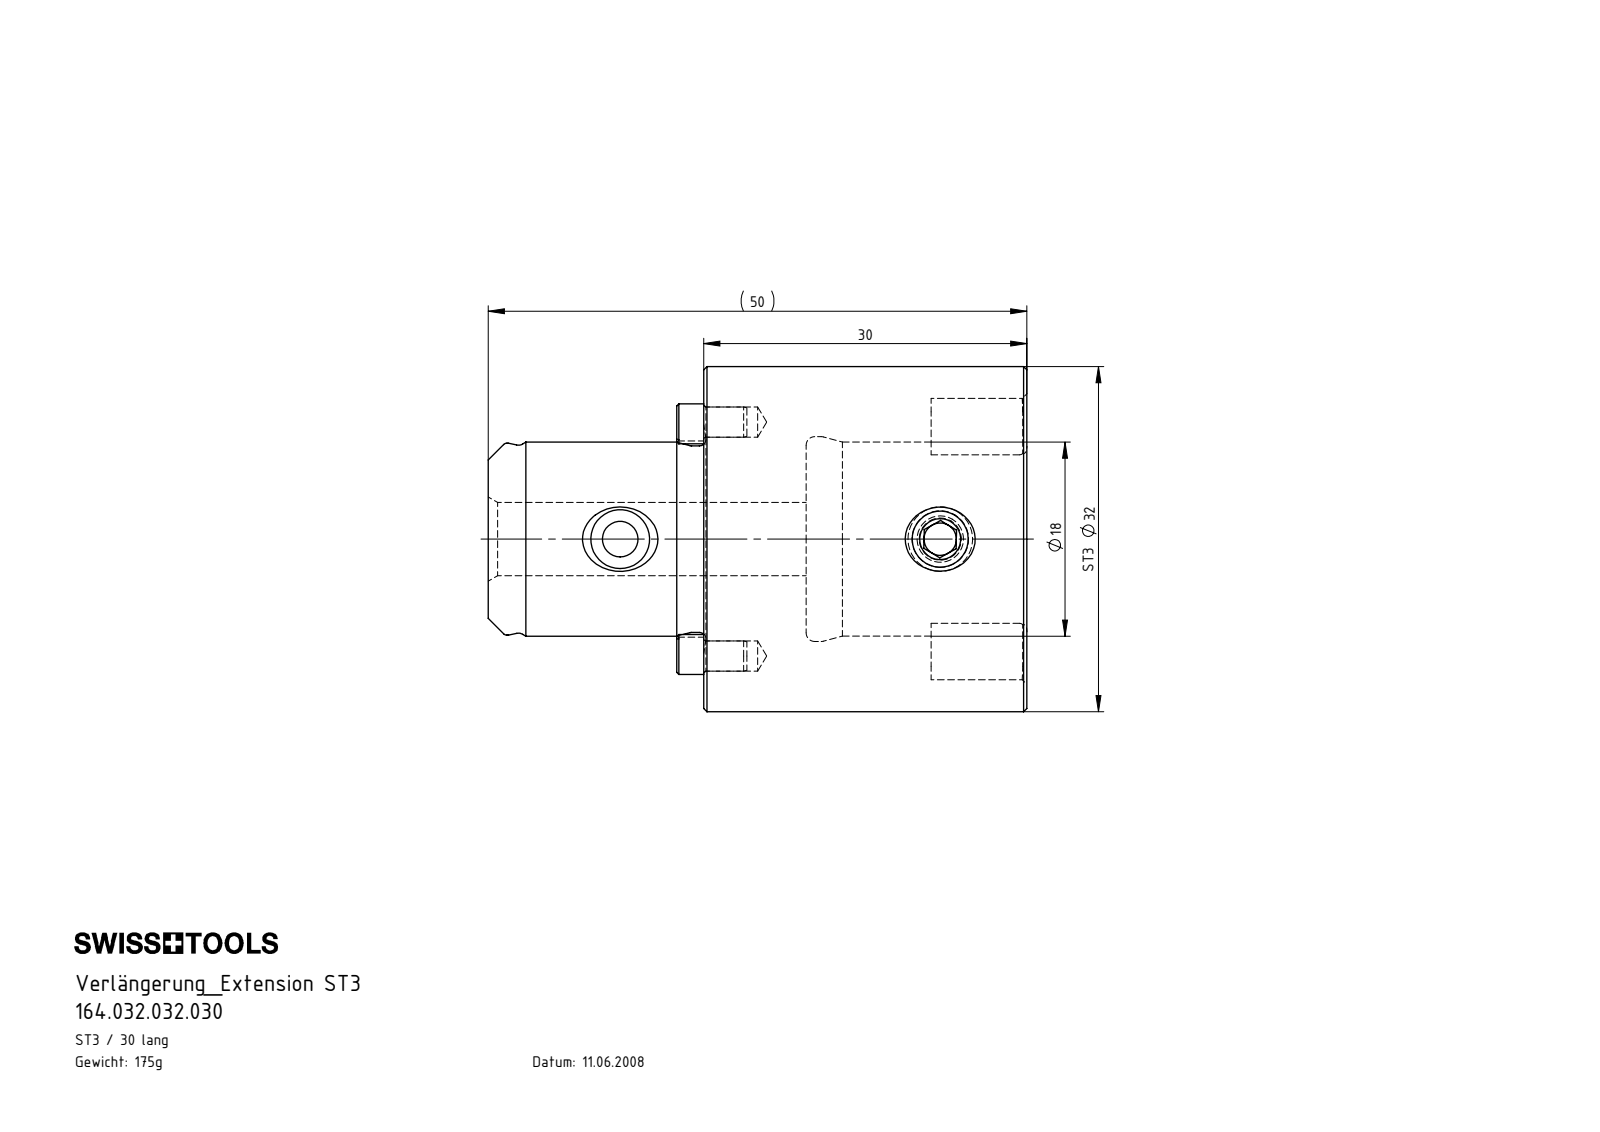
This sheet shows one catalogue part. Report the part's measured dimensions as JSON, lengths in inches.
{"part_name": "ST3-ST3.K01.030; ST3-ER2.001.007_A; ST3-ER1.001.008_A; ST3-ST3.K01.030_B", "step_written_by": "SolidWorks 2017 (CONFIG_CONTROL_DESIGN)", "units": "inches", "bodies": {"solids": 4, "faces": 160, "planar": 32, "cylindrical": 45, "other": 83}, "overall_size": [1.969, 1.26, 1.26], "volume_in3": 1.36, "surface_area_in2": 12.58, "round_holes": [[0.11, 2], [0.118, 1], [0.13, 1], [0.207, 1], [0.268, 1], [0.709, 1], [0.748, 1]], "round_bosses_or_shafts": [[1.26, 1], [0.701, 1], [0.681, 1], [0.236, 1]], "partial_cylinders_radius": [[0.02, 4], [0.098, 2], [0.107, 2], [0.356, 2]], "face_to_face_distances": [1.181, 0.374, 0.807, 0.787, 1.161, 1.969, 0.612, 1.618, 0.831, 0.457], "hole_center_spacings": [0.427, 0.854, 1.169]}
